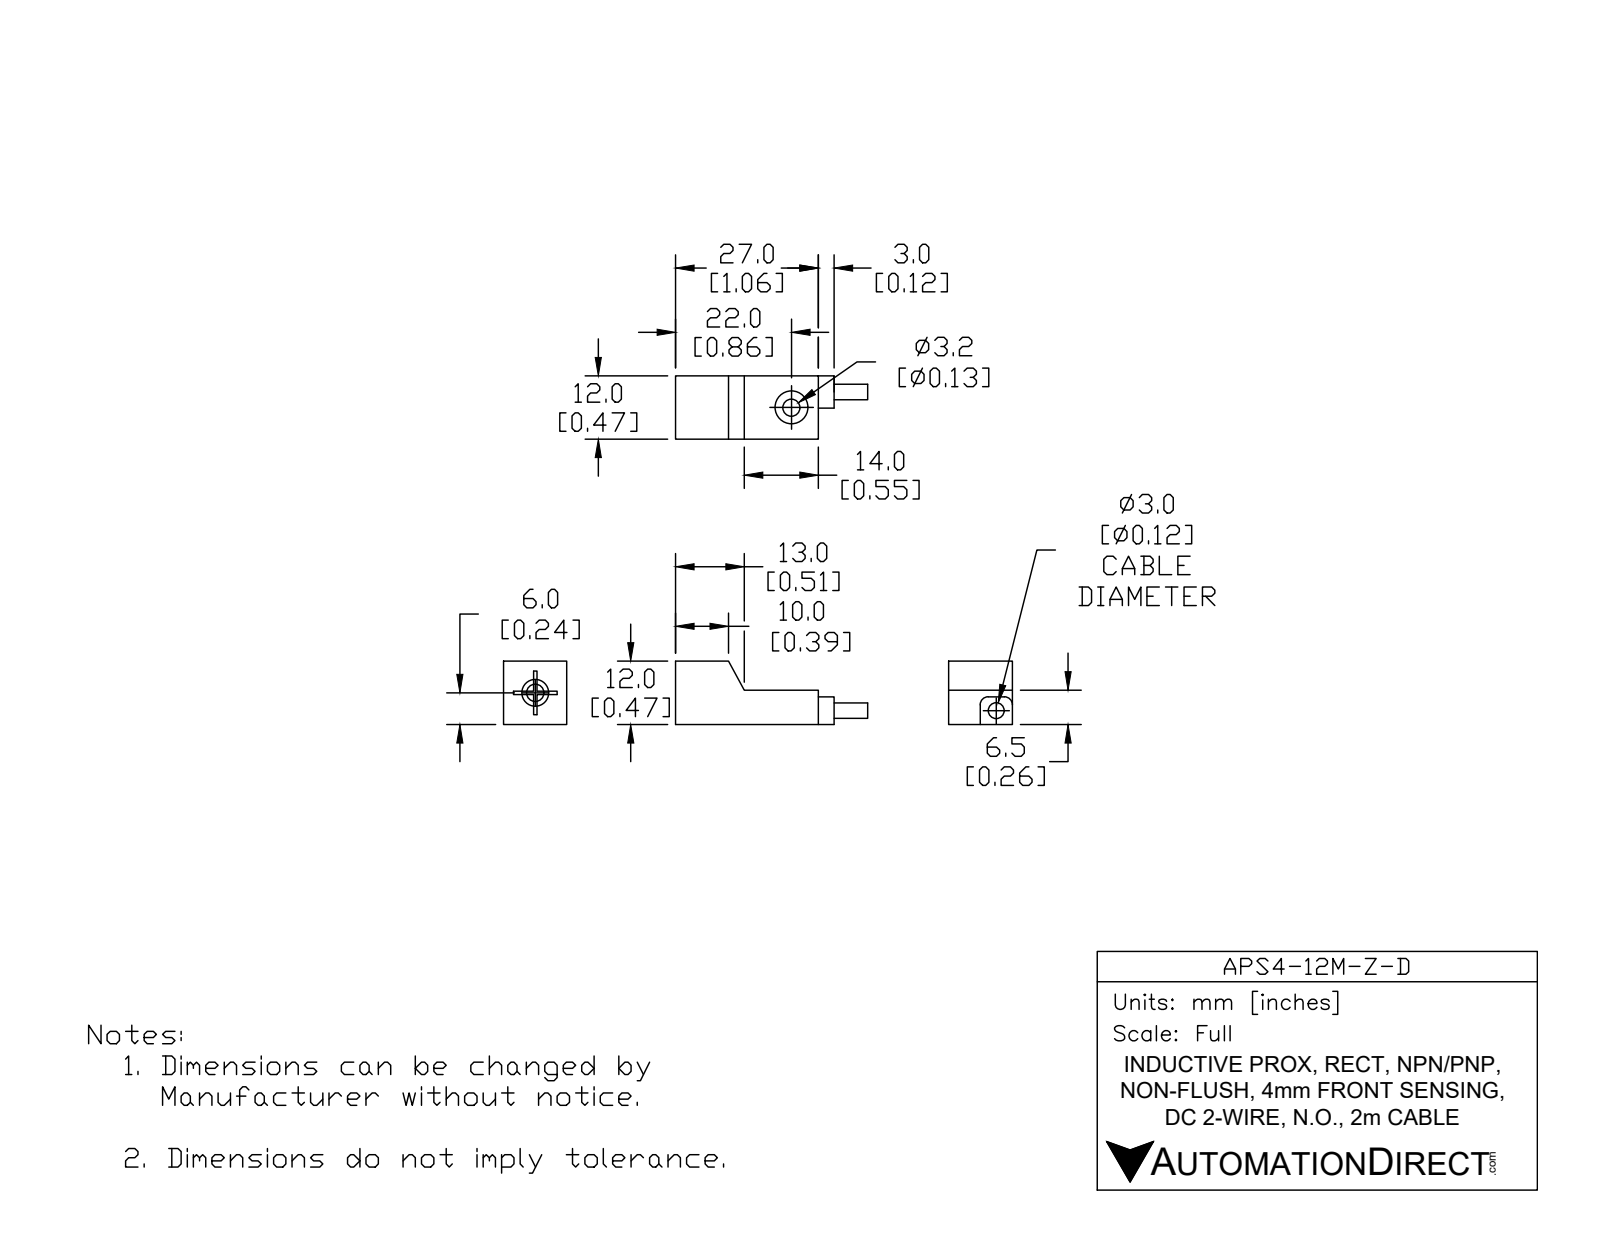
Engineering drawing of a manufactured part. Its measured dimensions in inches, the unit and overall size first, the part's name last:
Units: inches
Overall size (bounding box): 1.606 × 0.516 × 0.485
Round holes (diameter × count): ⌀0.081 ×1, ⌀0.126 ×1, ⌀0.205 ×1, ⌀0.217 ×1, ⌀0.23 ×1
Round bosses / shafts (diameter × count): ⌀0.226 ×1, ⌀0.112 ×1
Partial cylindrical surfaces — rounded edges, fillets, slot ends (radius × count): R0.005 ×8, R0.02 ×4, R0.031 ×2
Main face-to-face distances: 0.05, 0.273, 0.422, 0.261, 0.472, 0.285, 0.022, 0.251, 0.263, 0.211
Hole centre spacings: 0.629
Volume: 0.101 in³ · Surface area: 5.969 in²
Bodies: 4 solids, 100 faces (72 planar, 28 cylindrical, 0 other)
Part name (STEP PRODUCT): APS4-12M-Z-D
STEP written by: SolidWorks 2017 (AUTOMOTIVE_DESIGN)
